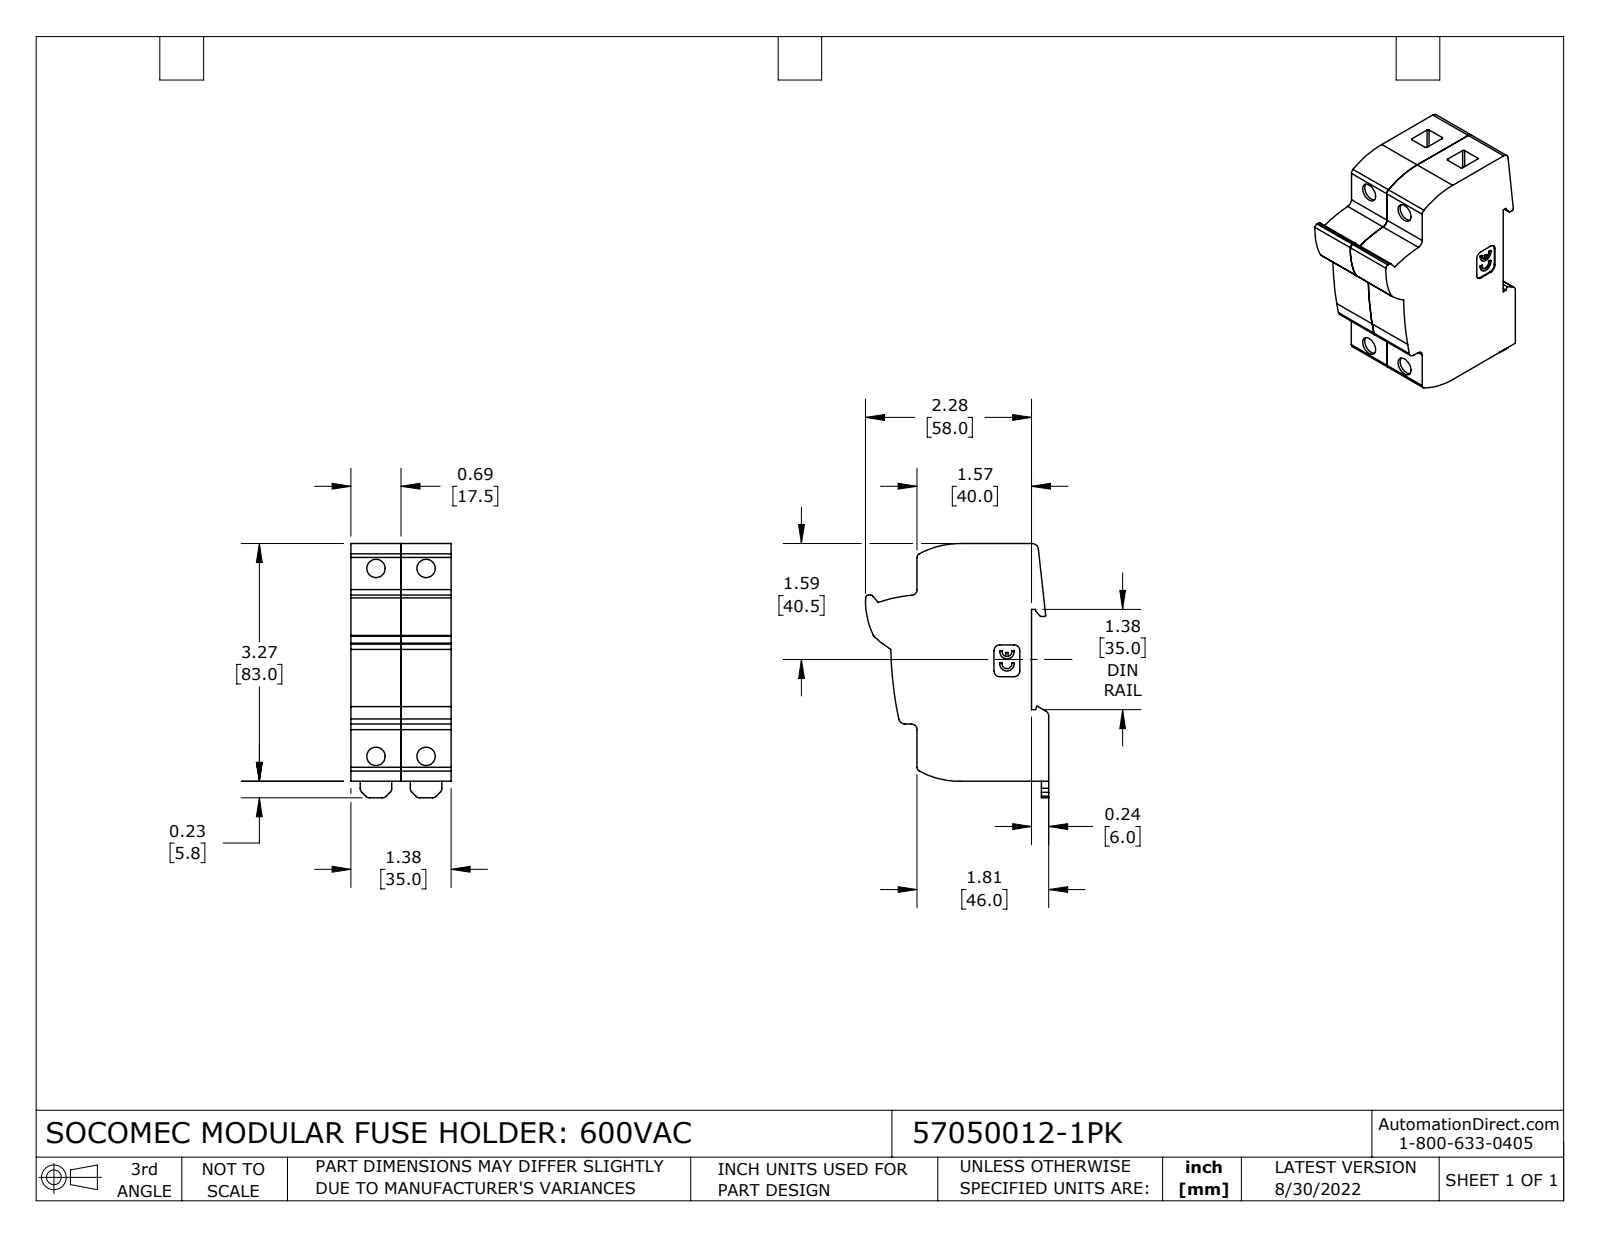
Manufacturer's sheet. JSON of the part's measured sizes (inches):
{"part_name": "57050012-1PK", "step_written_by": "SolidWorks 2021 (CONFIG_CONTROL_DESIGN)", "units": "inches", "bodies": {"solids": 2, "faces": 210, "planar": 104, "cylindrical": 106, "other": 0}, "overall_size": [3.496, 2.52, 1.378], "volume_in3": 8.458, "surface_area_in2": 42.66, "round_holes": [[0.252, 4]], "partial_cylinders_radius": [[0.079, 15], [0.02, 9], [0.039, 4], [0.059, 2], [0.067, 2], [0.087, 2], [0.098, 2], [1.186, 2]], "face_to_face_distances": [0.689, 1.378, 0.236, 1.575, 3.268, 1.811, 0.199, 0.49, 0.888, 1.179], "hole_center_spacings": [0.689, 2.583, 2.673]}
